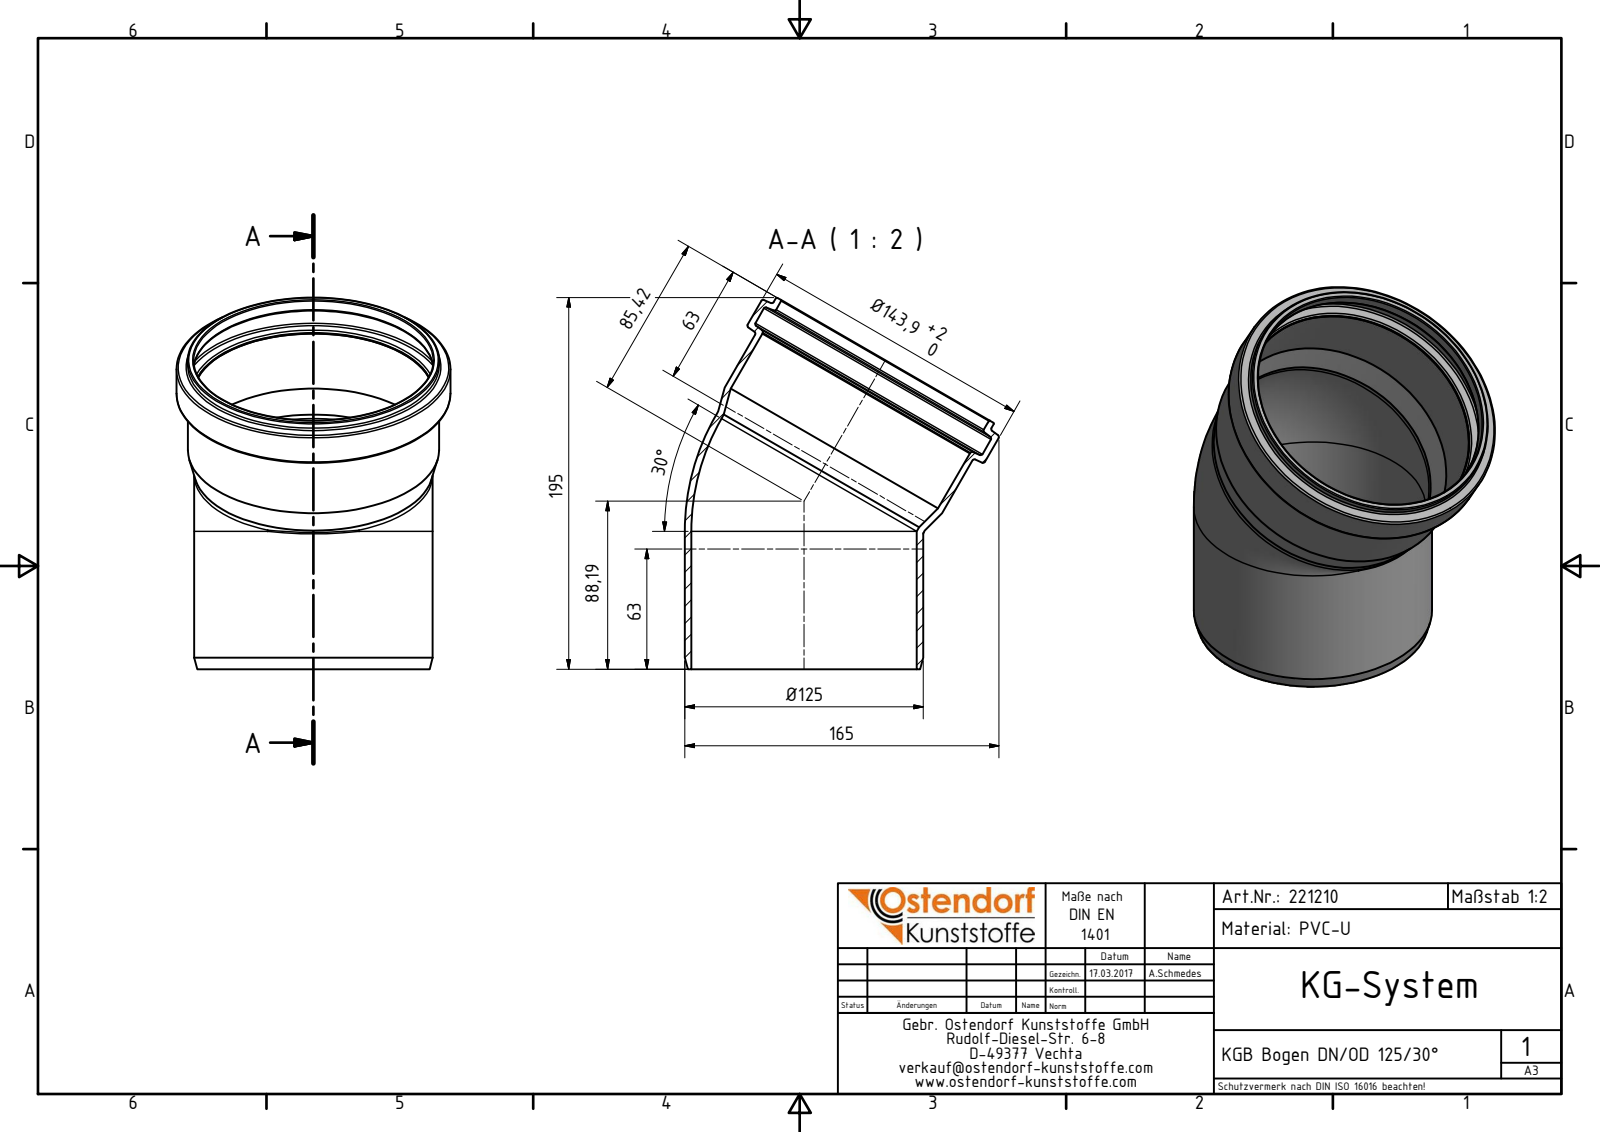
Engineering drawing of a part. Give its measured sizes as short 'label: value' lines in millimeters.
name: 221210 KGB Bogen DN_OD 125_30°
written by: Autodesk Inventor 2016 (AUTOMOTIVE_DESIGN)
unit: mm
bodies: 1 solid, 34 faces (3 planar, 11 cylindrical, 20 other)
size: 195 × 165 × 143.9
volume: 232 204 mm³; area: 146 223 mm²
holes: 2× ⌀118.4, 1× ⌀125.7, 1× ⌀125.9, 1× ⌀137.7
bosses: 2× ⌀125.2, 1× ⌀143.9, 1× ⌀132.1, 1× ⌀131.9
face distances: 20.17
